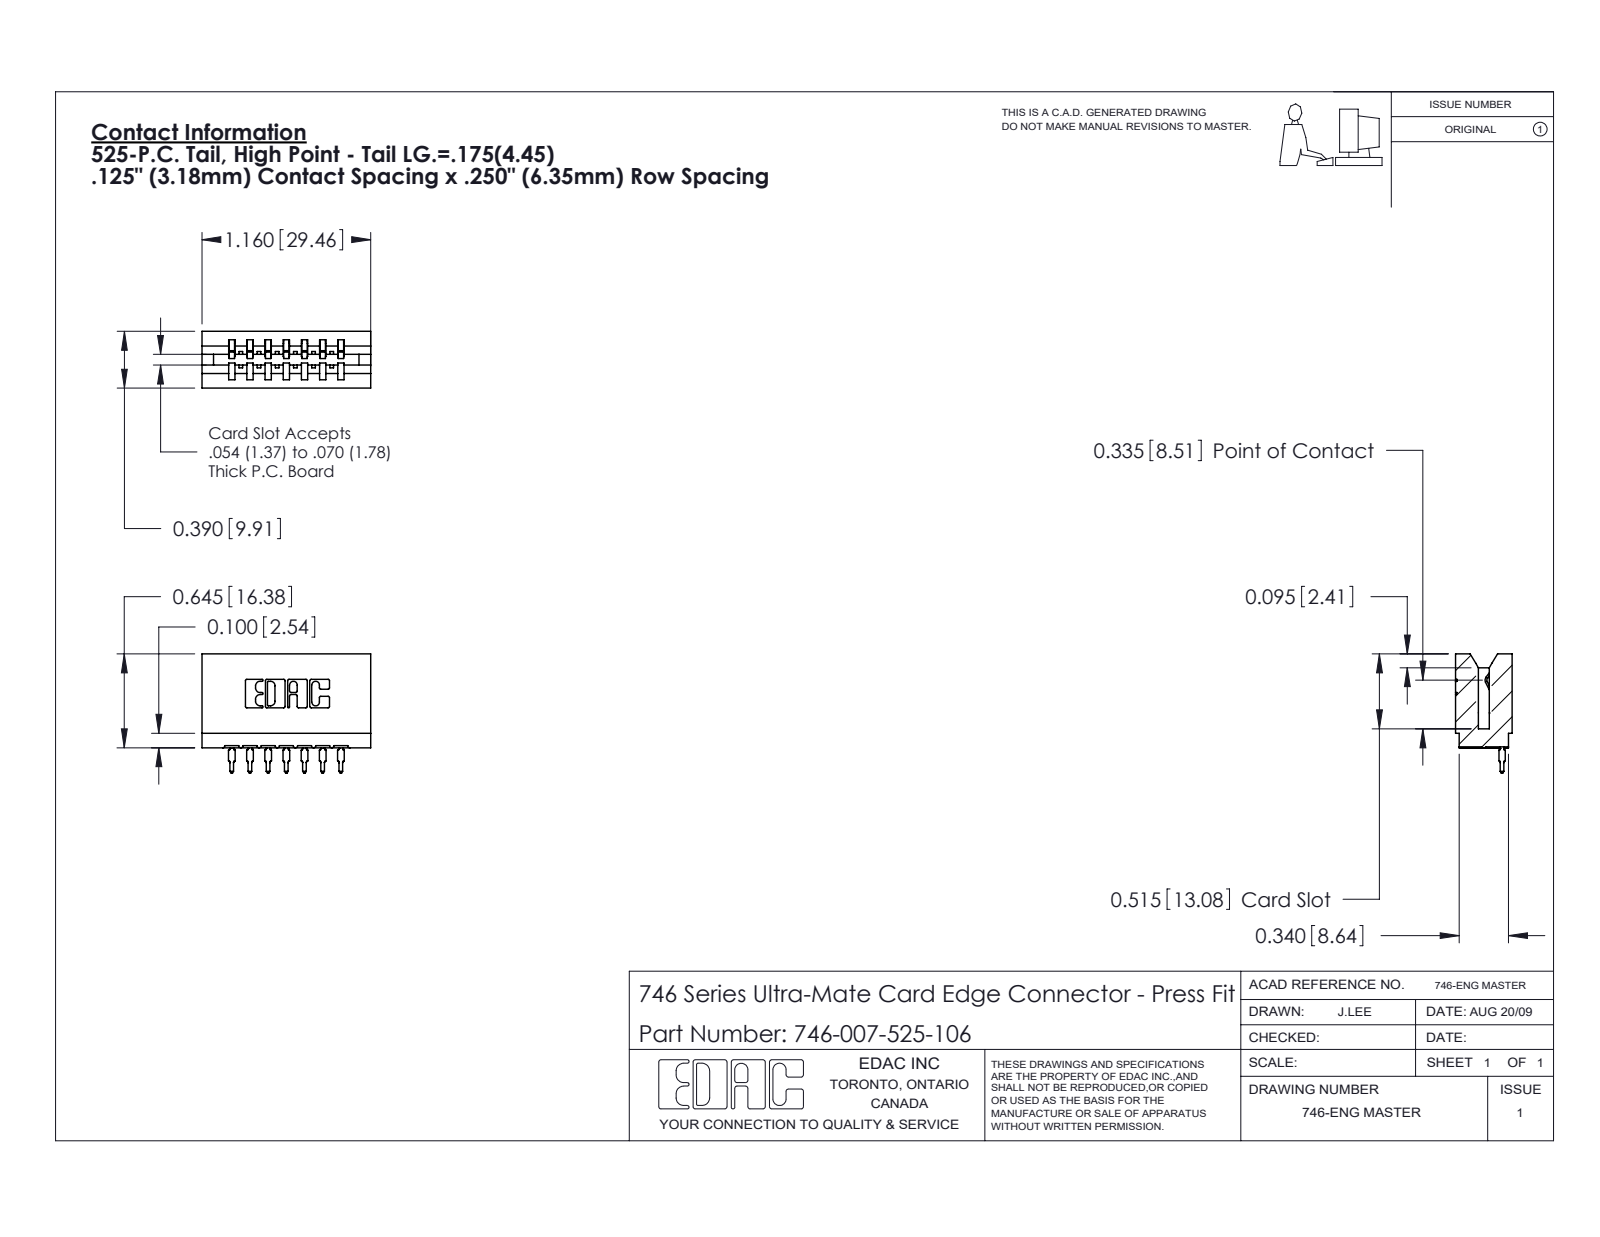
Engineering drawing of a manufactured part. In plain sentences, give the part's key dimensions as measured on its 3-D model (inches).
The part is named "746-292-001_525; 746 Part_.515 Slot Depth - 06; 746-007-525-106". Its 3-D file was written by "SolidWorks 2020 (CONFIG_CONTROL_DESIGN)". It is 8 solids with 854 faces: 497 planar, 175 cylindrical and 182 other. Overall it measures 1.16 by 0.819 by 0.39 inches. Its volume is 0.201 cubic inches and its surface area 6.607 square inches. Partial cylindrical surfaces (rounded edges, fillets, slot ends): 22 of radius 0.01, 14 of radius 0.021, 8 of radius 0.015, 6 of radius 0.007, 6 of radius 0.031, 4 of radius 0.005, 4 of radius 0.011, 3 of radius 0.026. The main face-to-face distances are 0.25, 0.042, 0.333, 0.5, 0.125, 0.125, 0.057, 0.208, 0.292, 0.39.
